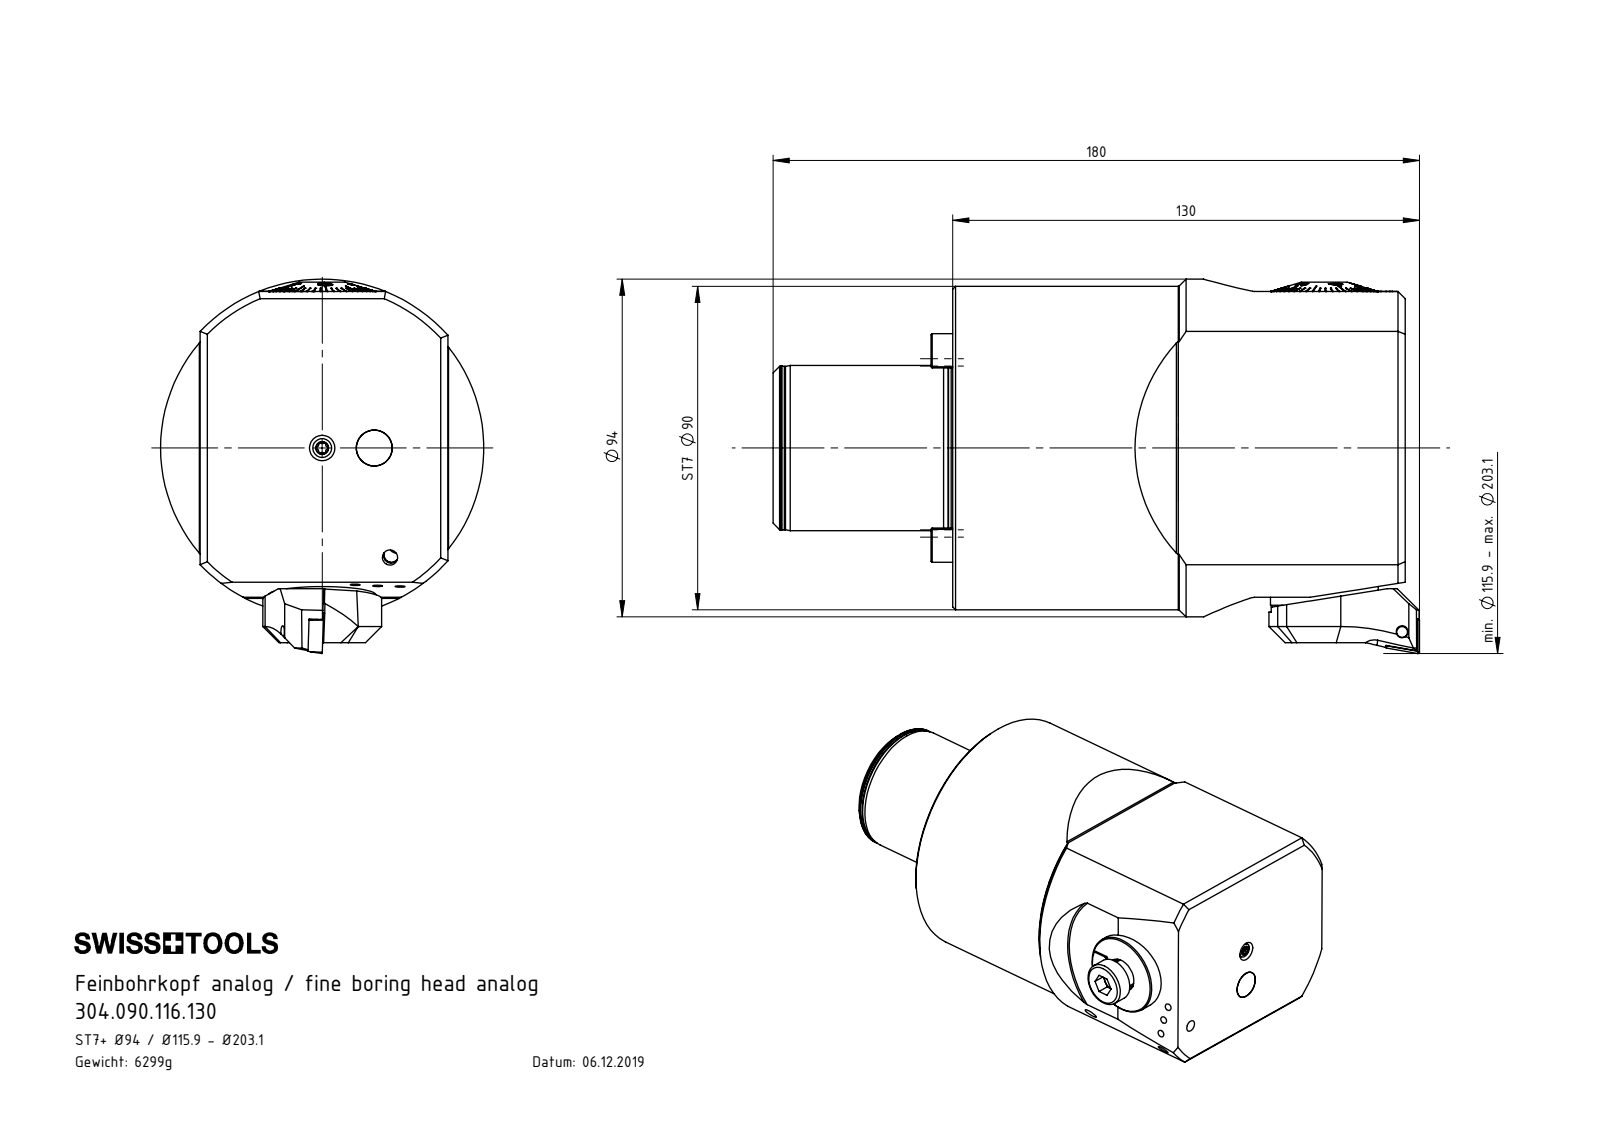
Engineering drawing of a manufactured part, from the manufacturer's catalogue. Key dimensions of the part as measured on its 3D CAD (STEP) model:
Part name (STEP PRODUCT): WCB-ER2.001.009_A; CCMT060204; ST7-F94.K21.130; F55-WCA.001.013 (+6 more)
STEP written by: SolidWorks 2015 (CONFIG_CONTROL_DESIGN)
Units: millimetres
Bodies: 8 solids, 381 faces (103 planar, 124 cylindrical, 154 other)
Overall size (bounding box): 180 × 106.03 × 94
Volume: 839 609 mm³ · Surface area: 82 123 mm²
Round holes (diameter × count): ⌀3.3 ×6, ⌀6 ×2, ⌀2 ×1, ⌀2.05 ×1, ⌀2.8 ×1, ⌀3.85 ×1, ⌀4.2 ×1, ⌀5 ×1, ⌀8.5 ×1, ⌀10 ×1, ⌀11 ×1, ⌀15 ×1
Round bosses / shafts (diameter × count): ⌀94 ×1, ⌀46 ×1, ⌀45.8 ×1, ⌀45.3 ×1, ⌀16 ×1, ⌀10 ×1, ⌀9.95 ×1, ⌀5.25 ×1
Partial cylindrical surfaces — rounded edges, fillets, slot ends (radius × count): R0.21 ×6, R0.34 ×6, R0.59 ×6, R0.36 ×5, R1 ×4, R3.2 ×3, R15 ×2, R0.36 ×1
Main face-to-face distances: 126, 50, 176, 89.53, 4, 93.53, 2.99, 1.5, 2.5, 91.03
Hole centre spacings: 28, 31.53, 4.22, 4.31, 14.5, 22.54, 32.5, 34.81
